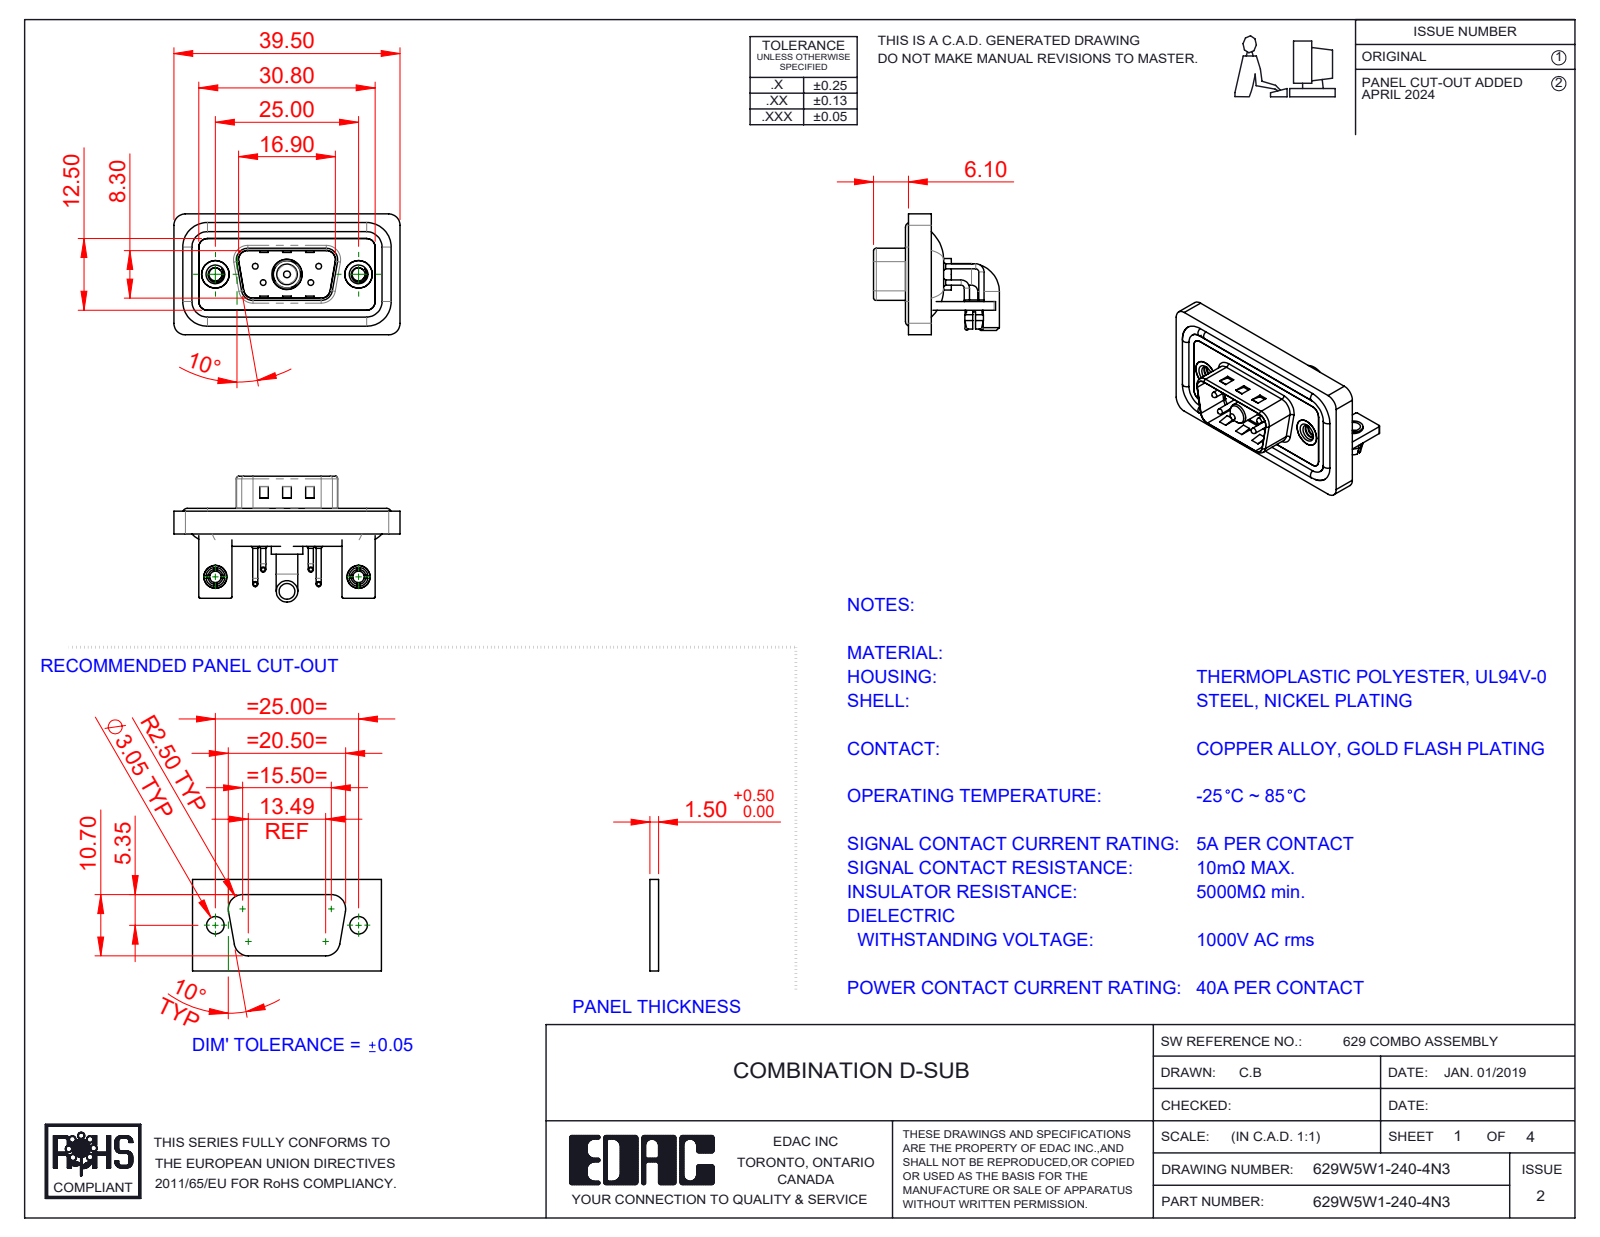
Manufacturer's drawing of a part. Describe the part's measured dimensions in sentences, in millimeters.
The part is named "629W5W1-140-4N3; 629Combo Board Lock; 629Combo Contact Row 1; 629Combo Threaded Rivet_3 (+7 more)". Its 3-D file was written by "SolidWorks 2023 (CONFIG_CONTROL_DESIGN)". It is 17 solids with 1026 faces: 479 planar, 395 cylindrical and 152 other. Overall it measures 39.5 by 21.98 by 21.1 millimeters. Its volume is 4 863 cubic millimeters and its surface area 8 005 square millimeters. Round holes: 6 of diameter 2, 4 of diameter 0.75, 4 of diameter 1.6, 2 of diameter 2.26, 2 of diameter 2.5, 2 of diameter 3.2, 2 of diameter 4, 2 of diameter 4.8, 2 of diameter 5, 1 of diameter 4.85, 1 of diameter 5.3. Round bosses or shafts: 8 of diameter 0.9, 4 of diameter 1.6, 4 of diameter 1.5, 4 of diameter 1, 4 of diameter 0.65, 2 of diameter 4.9, 2 of diameter 4, 2 of diameter 3.75. Partial cylindrical surfaces (rounded edges, fillets, slot ends): 19 of radius 2, 18 of radius 1.5, 16 of radius 0.25, 9 of radius 0.5, 8 of radius 1.6, 4 of radius 0.6, 4 of radius 0.65, 4 of radius 0.9. The main face-to-face distances are 0.4, 1.5, 0.8, 2.9, 1.1, 2.1, 1.2, 1.6, 2.5, 3.7. The hole center spacings are 3.16, 5.72, 7.1, 12.5, 18.1, 25, 4.39, 4.4.
